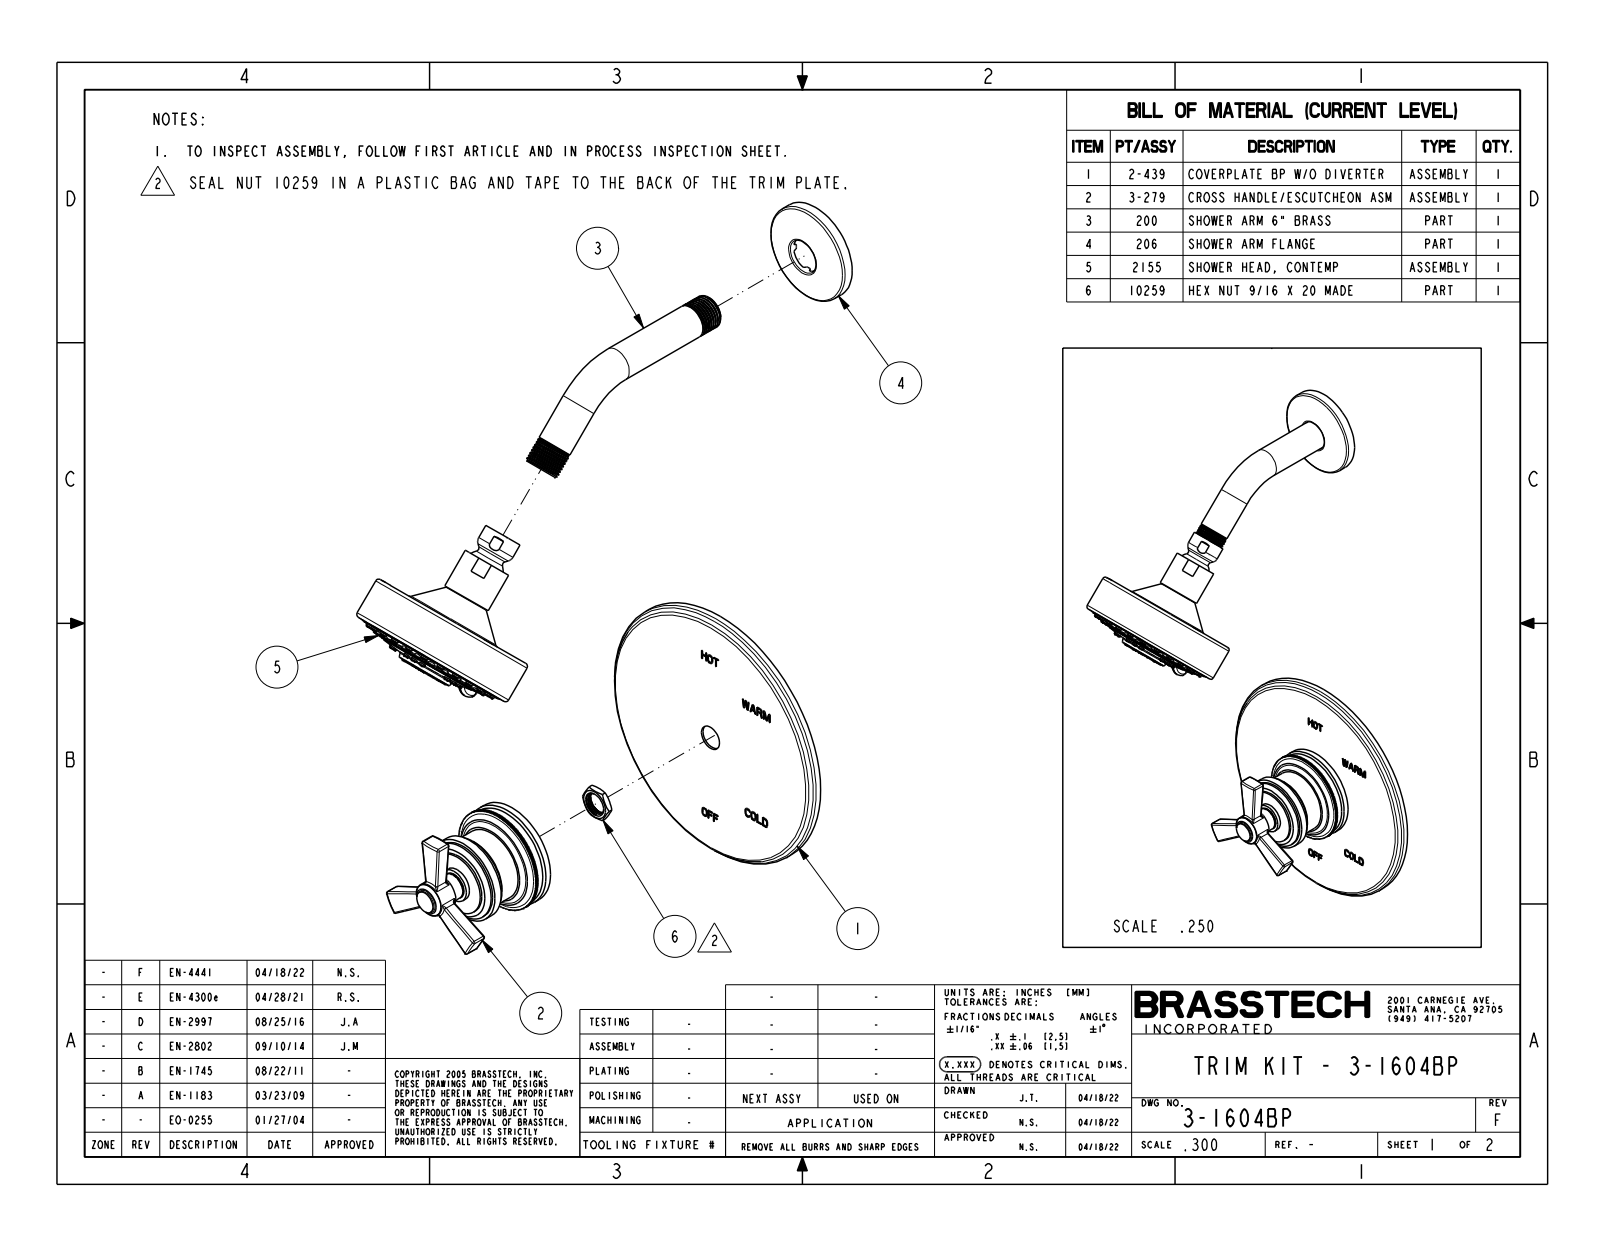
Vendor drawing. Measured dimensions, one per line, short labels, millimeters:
name: 3-1604BP
written by: CREO PARAMETRIC BY PTC INC, 2018400 (CONFIG_CONTROL_DESIGN)
unit: mm
bodies: 2 solids, 2068 faces (843 planar, 408 cylindrical, 817 other)
size: 417.6 × 207.6 × 165.1
volume: 613 400 mm³; area: 106 900 mm²
holes: 8× ⌀1.5, 1× ⌀23.5
bosses: 39× ⌀3.6, 23× ⌀4.2, 2× ⌀20.7, 1× ⌀165.1, 1× ⌀101.6, 1× ⌀94.6, 1× ⌀63.5, 1× ⌀61
rounds: 8× R2, 6× R1, 6× R2.5, 2× R0.5, 1× R3.5, 1× R12, 1× R13, 1× R16
face distances: 8, 53, 45.1, 5.1, 2.5, 29.1, 33, 3.8, 10.2, 34.9
hole spacings: 11.3, 14.7, 20.8, 20.8, 27.2, 11.3, 14.7, 27.2
